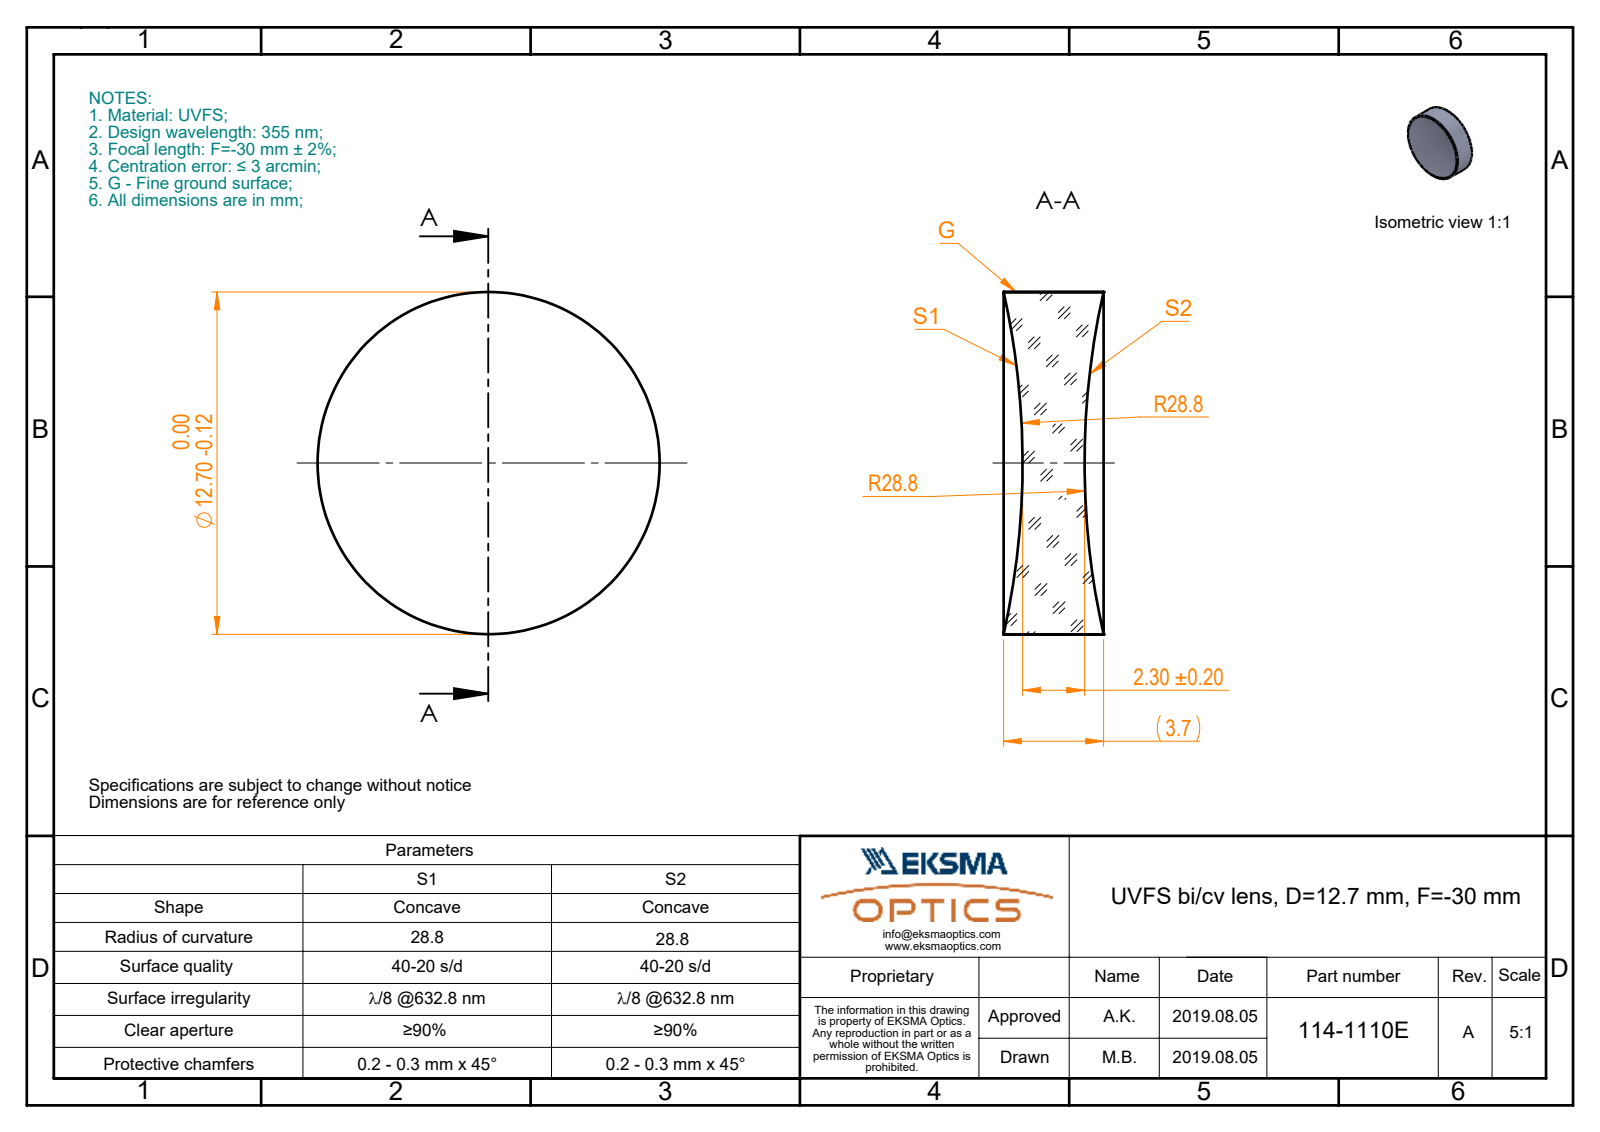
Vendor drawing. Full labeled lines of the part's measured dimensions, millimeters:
Part name (STEP PRODUCT): 114-1110E UVFS bi-cv 12.7 F-30
STEP written by: SolidWorks 2017 (CONFIG_CONTROL_DESIGN)
Units: millimetres
Bodies: 1 solid, 6 faces (0 planar, 2 cylindrical, 4 other)
Overall size (bounding box): 12.7 × 12.7 × 3.71
Volume: 380 mm³ · Surface area: 405 mm²
Round bosses / shafts (diameter × count): ⌀12.7 ×1
